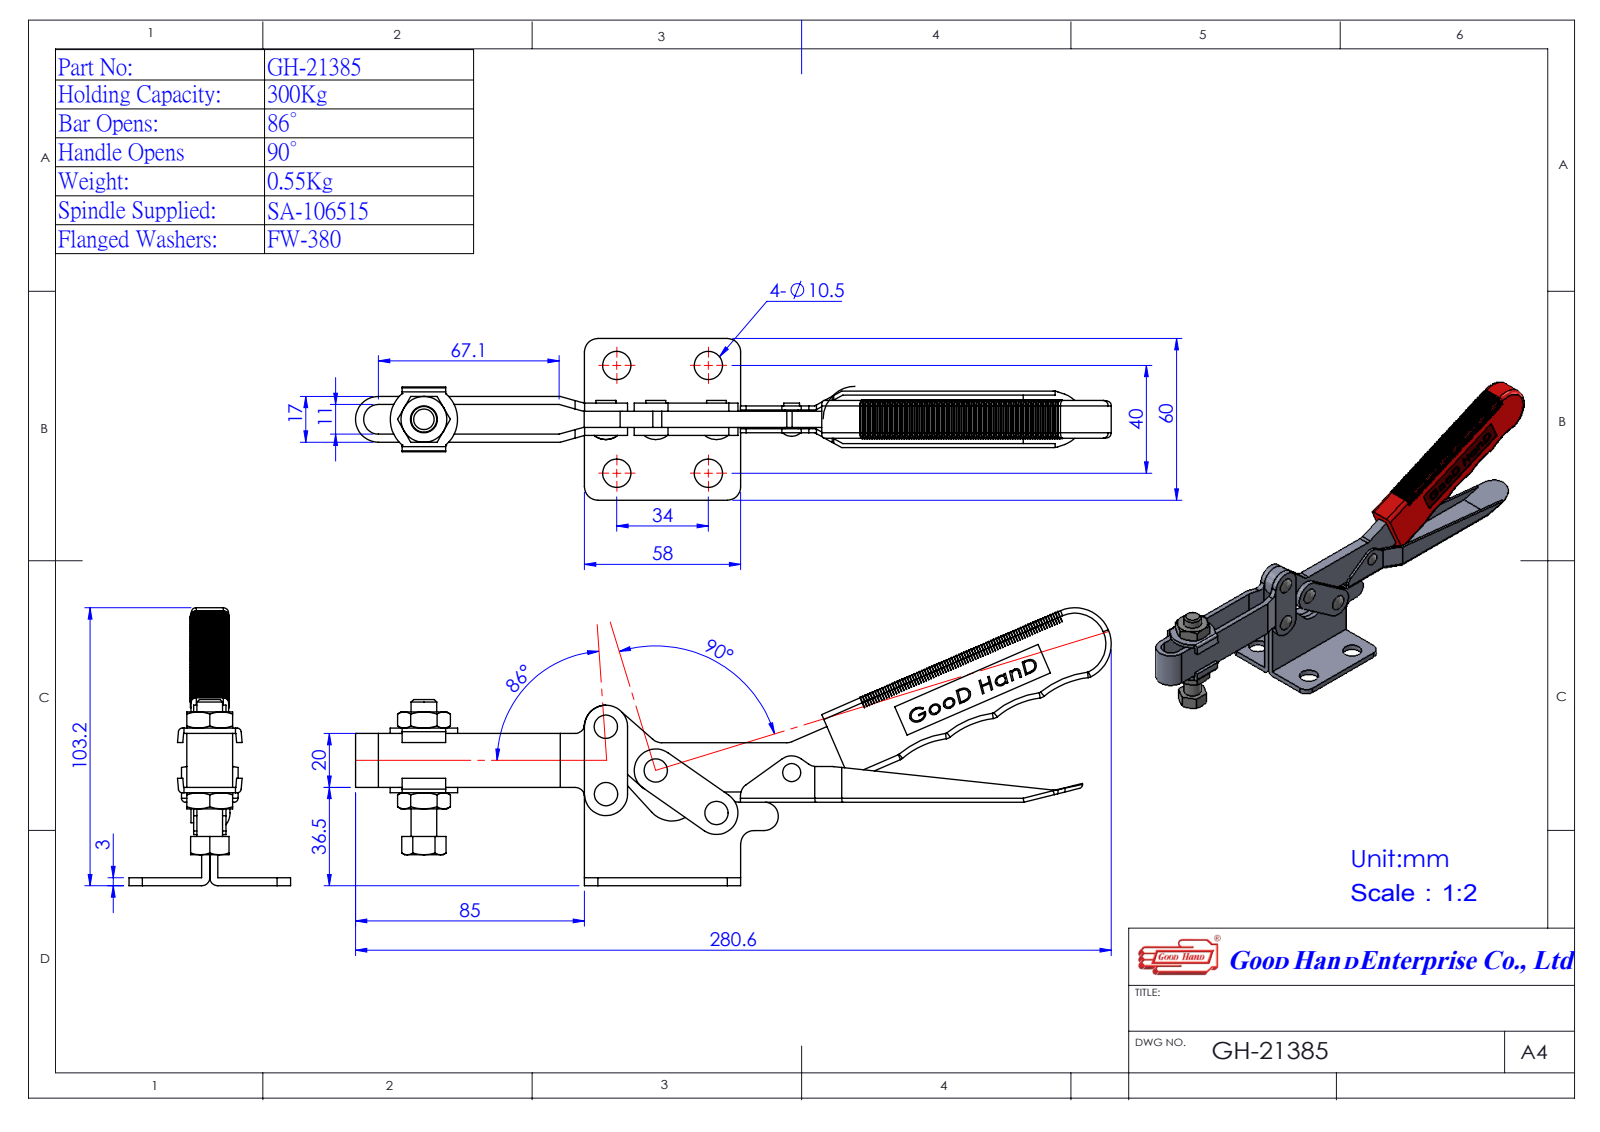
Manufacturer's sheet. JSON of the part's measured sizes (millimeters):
{"part_name": "Group4^GH-21385(簡化); Group5^GH-21385(簡化); Group1^GH-21385(簡化); Group2^GH-21385(簡化) (+2 more)", "step_written_by": "SolidWorks 2016 (AUTOMOTIVE_DESIGN)", "units": "millimeters", "bodies": {"solids": 6, "faces": 351, "planar": 152, "cylindrical": 145, "other": 54}, "overall_size": [280.57, 103.16, 60], "volume_mm3": 105055, "surface_area_mm2": 55157, "round_holes": [[5, 4], [10.5, 4], [6.33, 2], [10, 1]], "round_bosses_or_shafts": [[7.35, 4], [6.35, 2], [16, 1], [9.53, 1], [5.83, 1], [4.83, 1]], "partial_cylinders_radius": [[1.5, 14], [5, 12], [3, 6], [8, 5], [32, 4], [3.5, 2], [10, 2], [5.25, 1]], "face_to_face_distances": [3, 1.5, 14, 4, 10, 6, 2.5, 11.5, 2, 0.5], "hole_center_spacings": [34, 40, 52.5, 74.34, 107.48, 20.43, 24.65, 25]}
